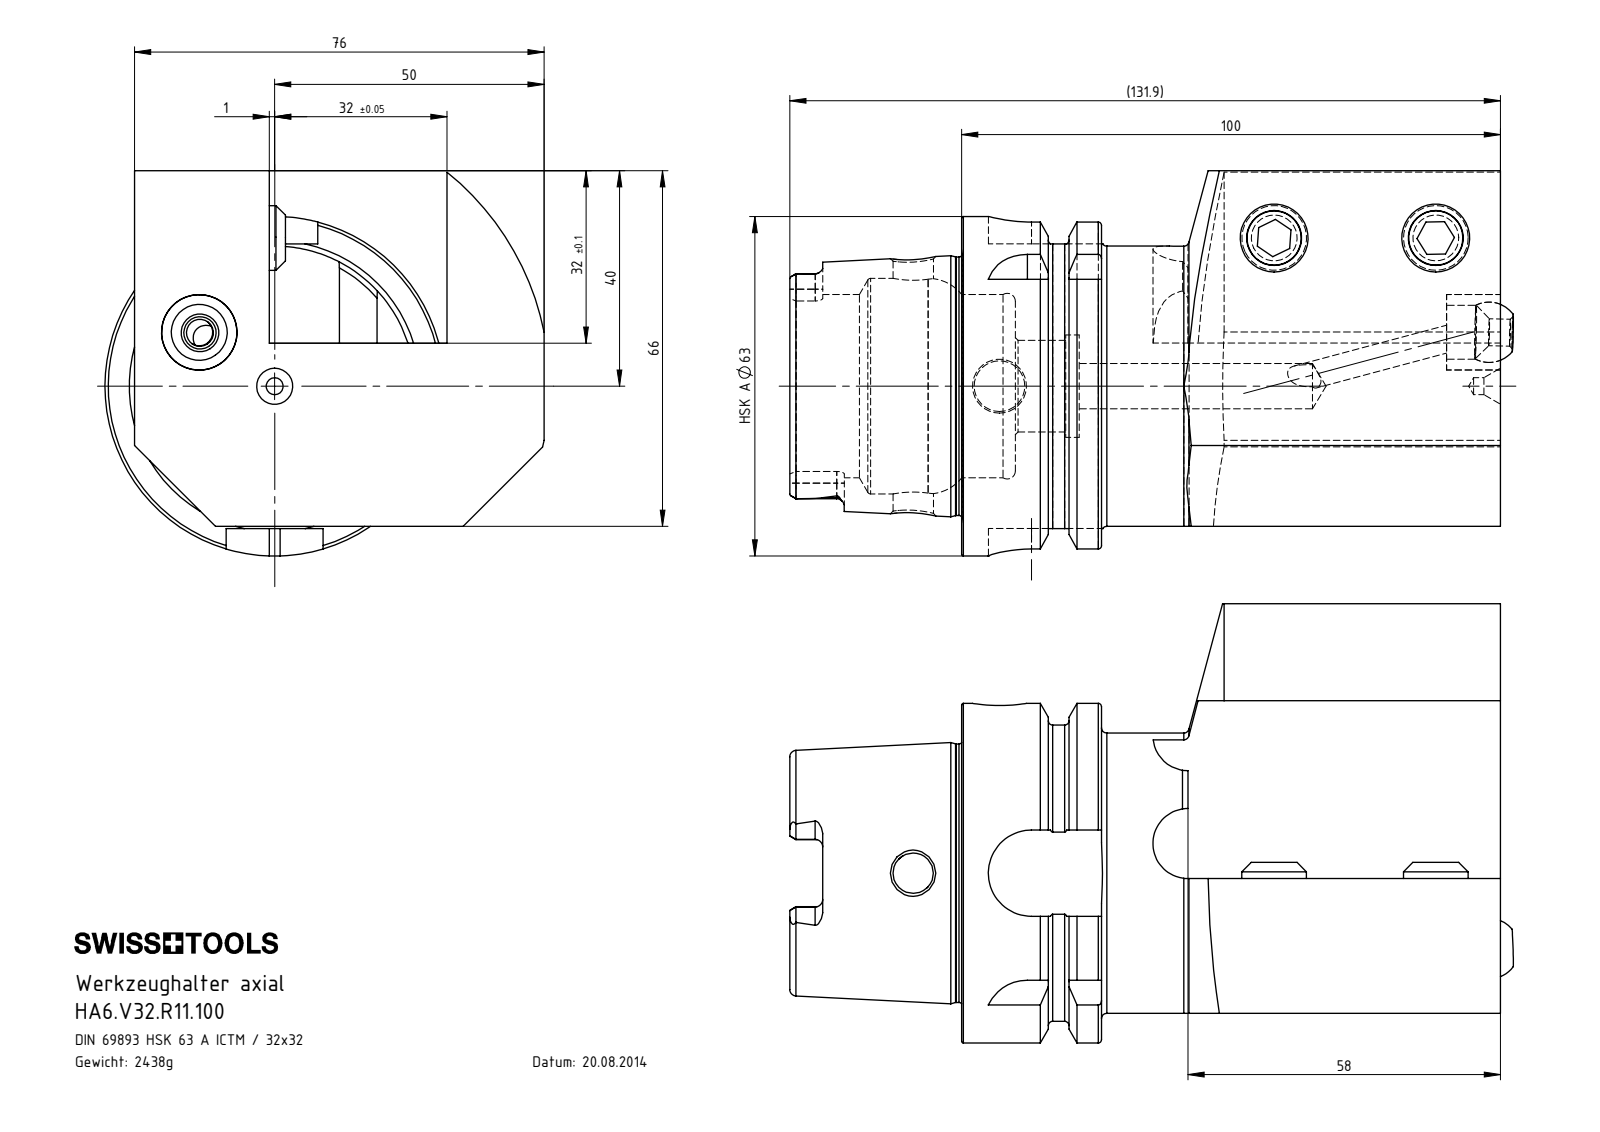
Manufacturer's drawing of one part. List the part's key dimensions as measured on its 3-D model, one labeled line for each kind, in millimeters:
Part name (STEP PRODUCT): HA6-V32.R11.100; KU1-U14.001.012; KU1-U14.001.012_2; KU1-U14.001.012_1 (+2 more)
STEP written by: SolidWorks 2012 (CONFIG_CONTROL_DESIGN)
Units: millimetres
Bodies: 5 solids, 242 faces (75 planar, 70 cylindrical, 97 other)
Overall size (bounding box): 134.3 × 81.5 × 71.5
Volume: 311 106 mm³ · Surface area: 53 046 mm²
Round holes (diameter × count): ⌀5 ×2, ⌀10 ×2, ⌀10.2 ×2, ⌀3.15 ×1, ⌀7.5 ×1, ⌀8.4 ×1, ⌀14 ×1, ⌀17 ×1, ⌀19 ×1, ⌀34 ×1, ⌀40 ×1
Round bosses / shafts (diameter × count): ⌀12 ×2, ⌀63 ×1, ⌀54.95 ×1, ⌀52 ×1, ⌀47.94 ×1
Partial cylindrical surfaces — rounded edges, fillets, slot ends (radius × count): R1.4 ×6, R2.88 ×4, R8 ×4, R6.5 ×2, R51 ×1
Main face-to-face distances: 34, 58, 25, 33, 32, 66, 18, 100, 51, 76
Hole centre spacings: 17.2, 30, 57.94, 85.54
